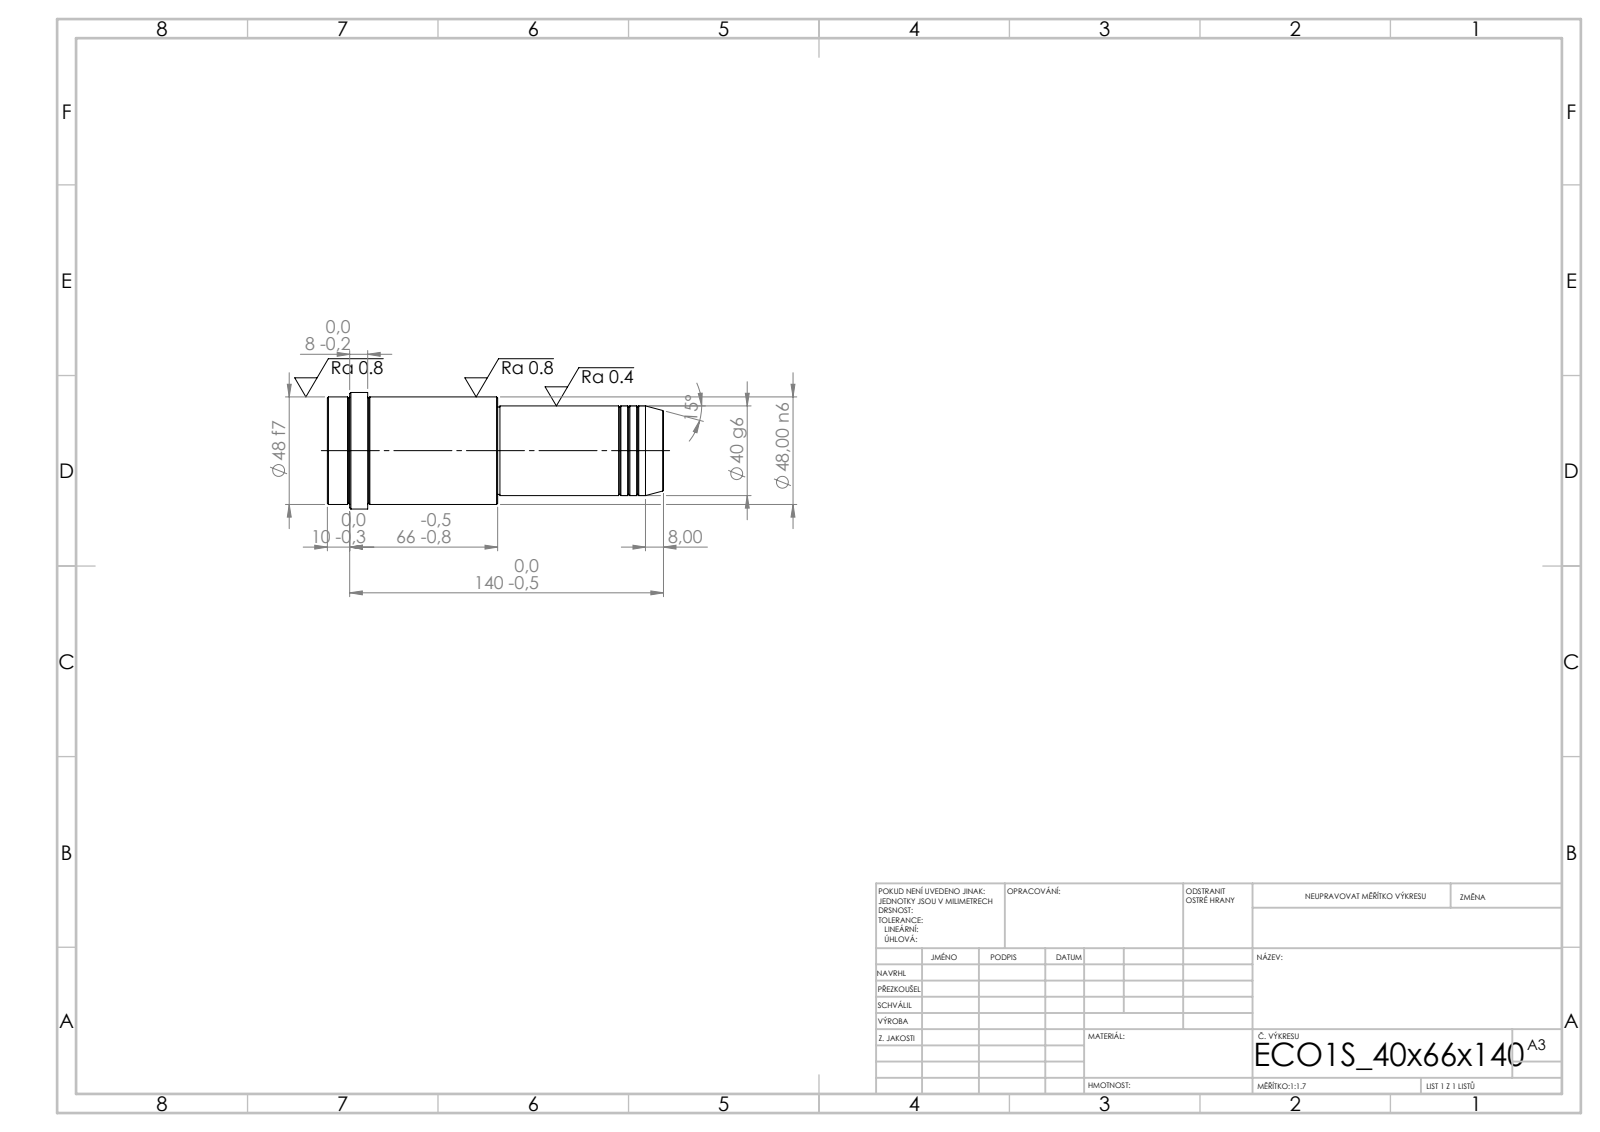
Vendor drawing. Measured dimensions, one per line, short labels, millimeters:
written by: SolidWorks 2019 (CONFIG_CONTROL_DESIGN)
unit: mm
bodies: 1 solid, 52 faces (6 planar, 16 cylindrical, 30 other)
size: 150 × 52 × 52
volume: 231 605 mm³; area: 25 175 mm²
bosses: 1× ⌀52, 1× ⌀48, 1× ⌀40, 1× ⌀39
face distances: 150, 74, 76, 132, 58, 18, 140, 66, 8, 10
